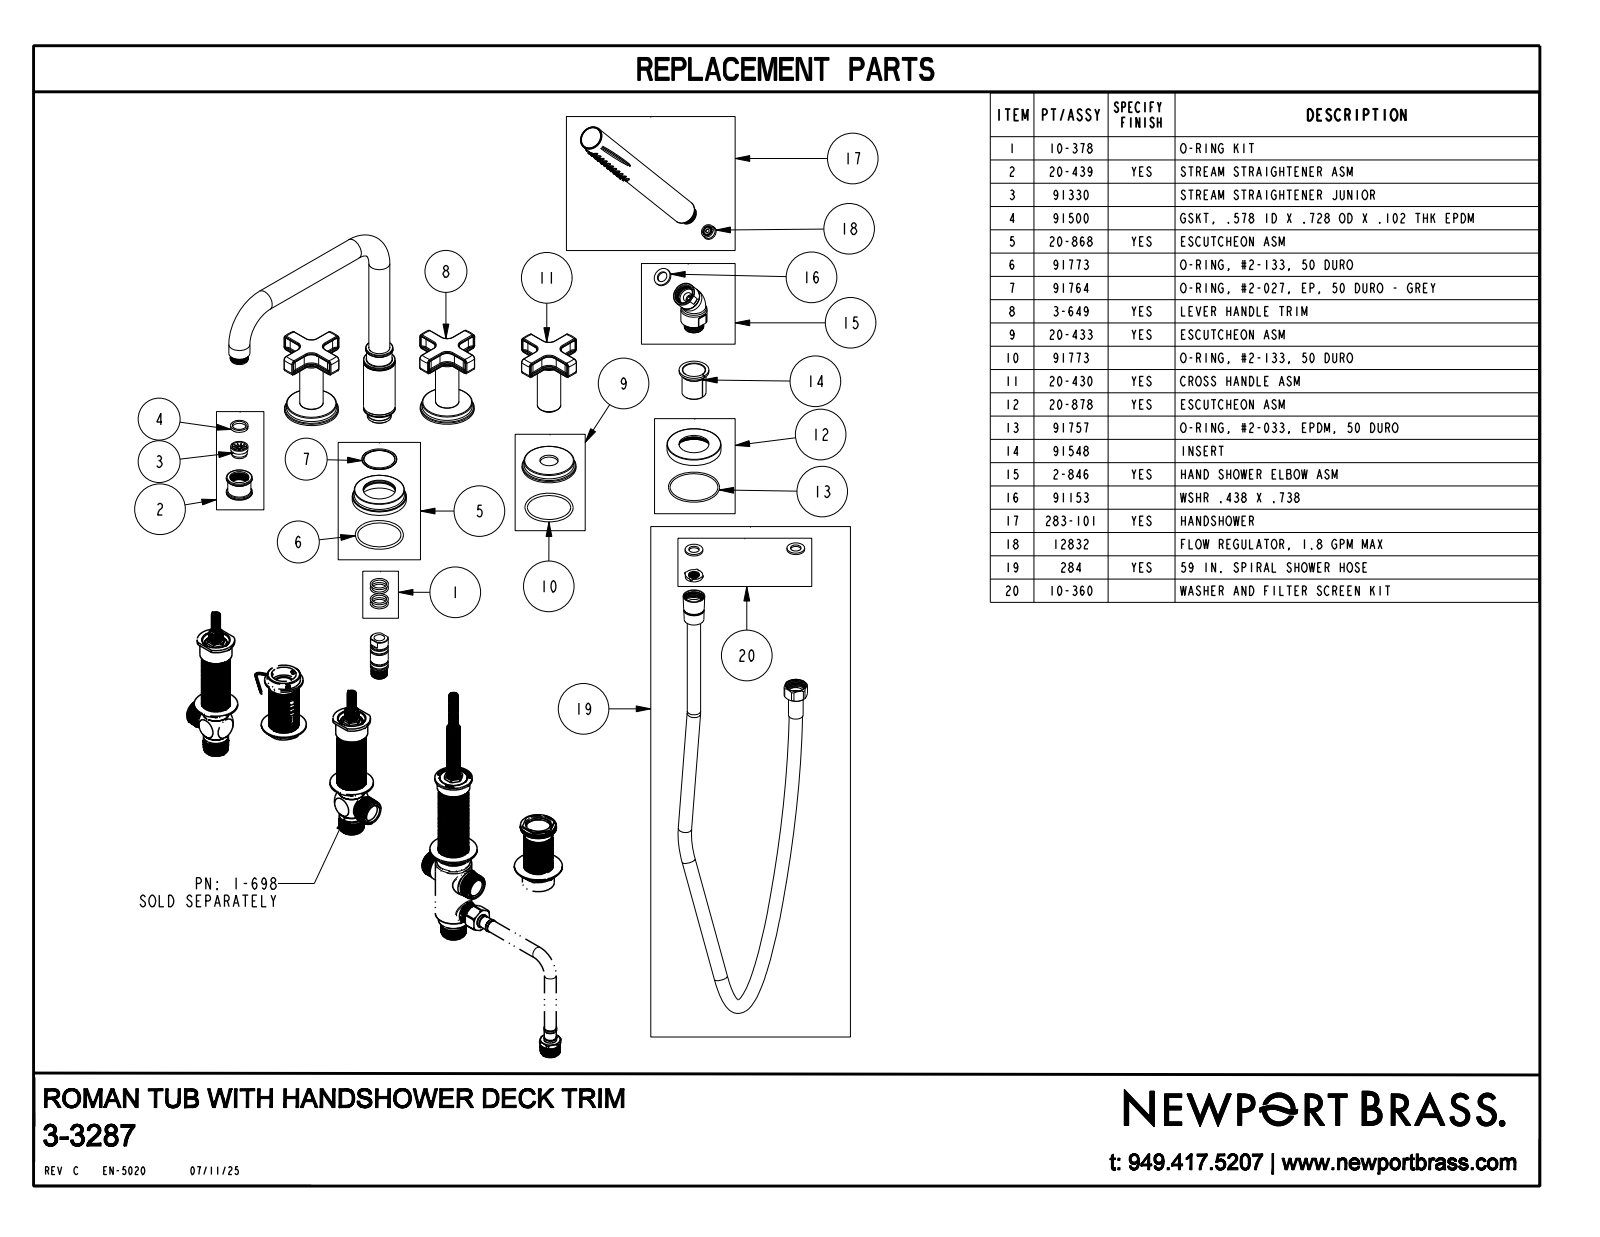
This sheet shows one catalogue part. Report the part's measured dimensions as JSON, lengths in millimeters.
{"part_name": "3-3287", "step_written_by": "CREO PARAMETRIC BY PTC INC, 2018400 (CONFIG_CONTROL_DESIGN)", "units": "millimeters", "bodies": {"solids": 5, "faces": 1574, "planar": 152, "cylindrical": 554, "other": 868}, "overall_size": [521.3, 258.8, 246.3], "volume_mm3": 612100, "surface_area_mm2": 133600, "round_holes": [[3.6, 44], [3, 1], [15.4, 1], [17.6, 1]], "round_bosses_or_shafts": [[57.2, 5], [53.1, 4], [24.8, 4], [22.2, 3], [21.6, 3], [12.9, 3], [33.7, 1], [29, 1]], "partial_cylinders_radius": [[0.8, 96], [6.4, 24], [8.3, 12], [10.8, 12], [1.3, 6], [35.6, 3], [7.6, 1], [11.4, 1]], "face_to_face_distances": [8.9, 82.6, 73.7, 64.8, 55.9, 17.8, 7.6, 2.5, 75, 1.3], "hole_center_spacings": [8.5, 17.1, 4.3, 7.4, 11.4, 15.3, 22.1, 8.6]}
